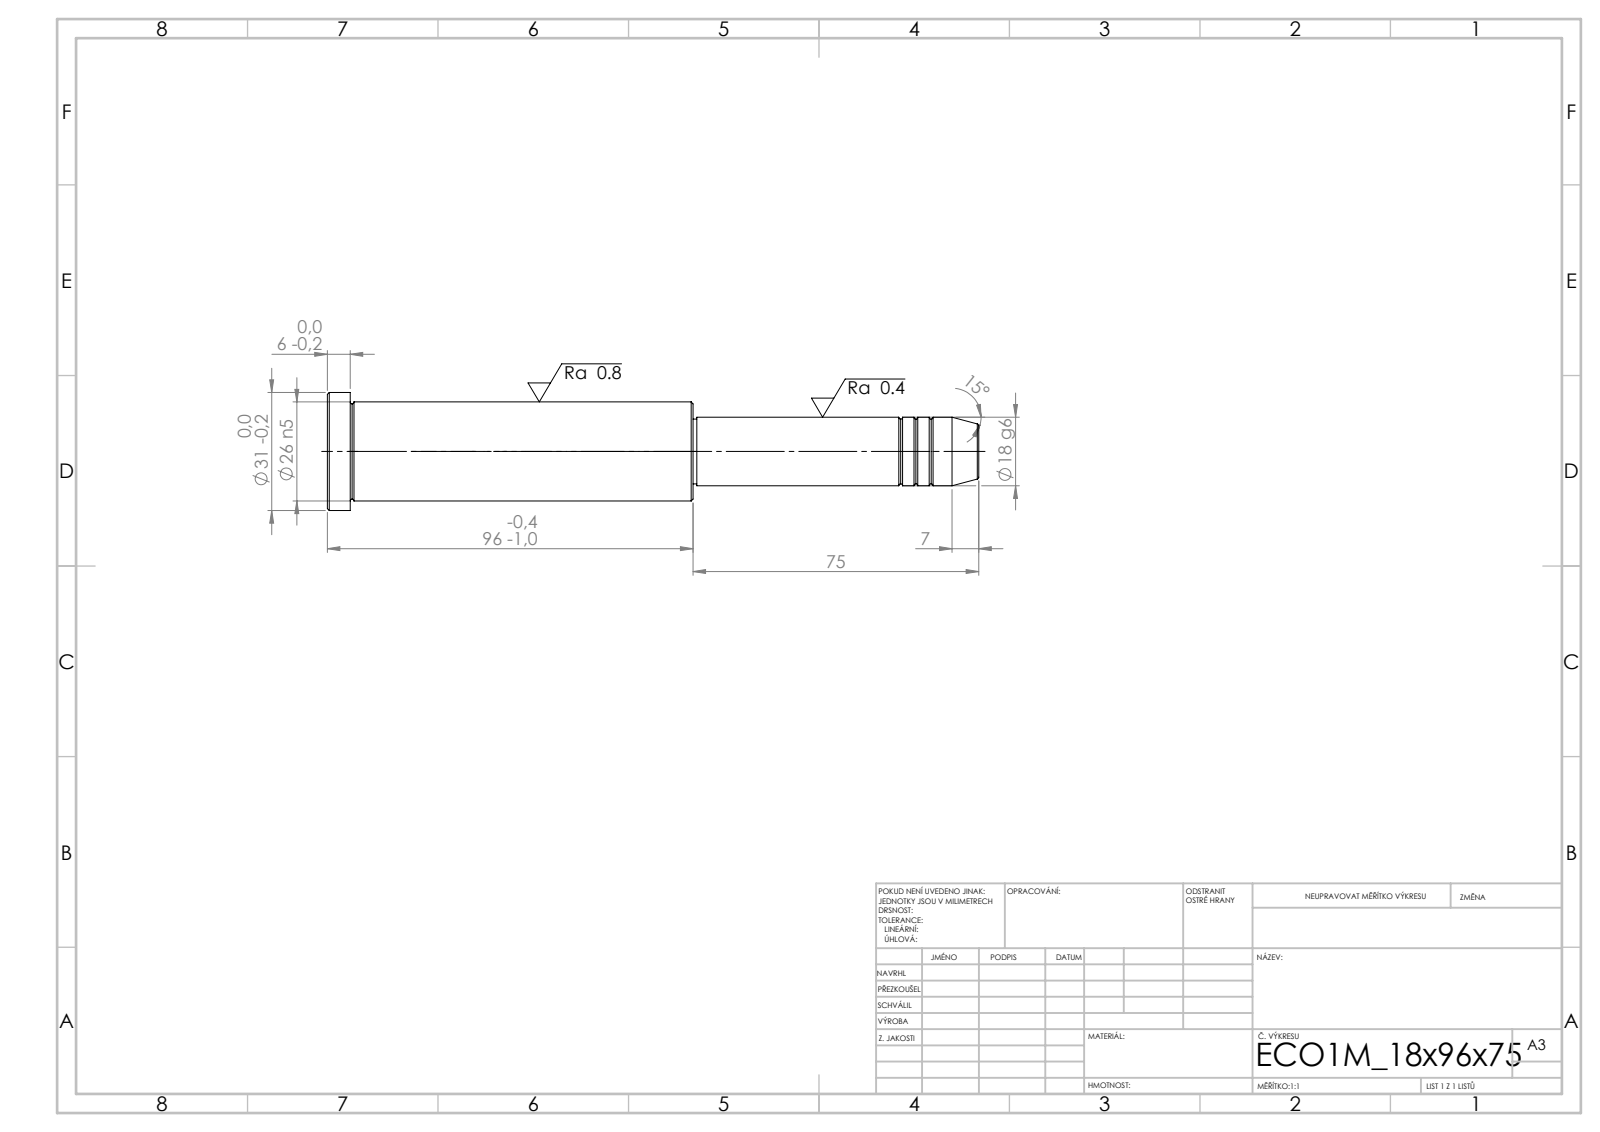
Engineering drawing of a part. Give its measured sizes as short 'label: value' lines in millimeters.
written by: SolidWorks 2019 (CONFIG_CONTROL_DESIGN)
unit: mm
bodies: 1 solid, 43 faces (5 planar, 14 cylindrical, 24 other)
size: 171 × 31 × 31
volume: 70 905 mm³; area: 13 687 mm²
bosses: 1× ⌀31, 1× ⌀26, 1× ⌀18, 1× ⌀17
face distances: 96, 90, 6, 75, 165, 171, 74, 1, 91, 97
